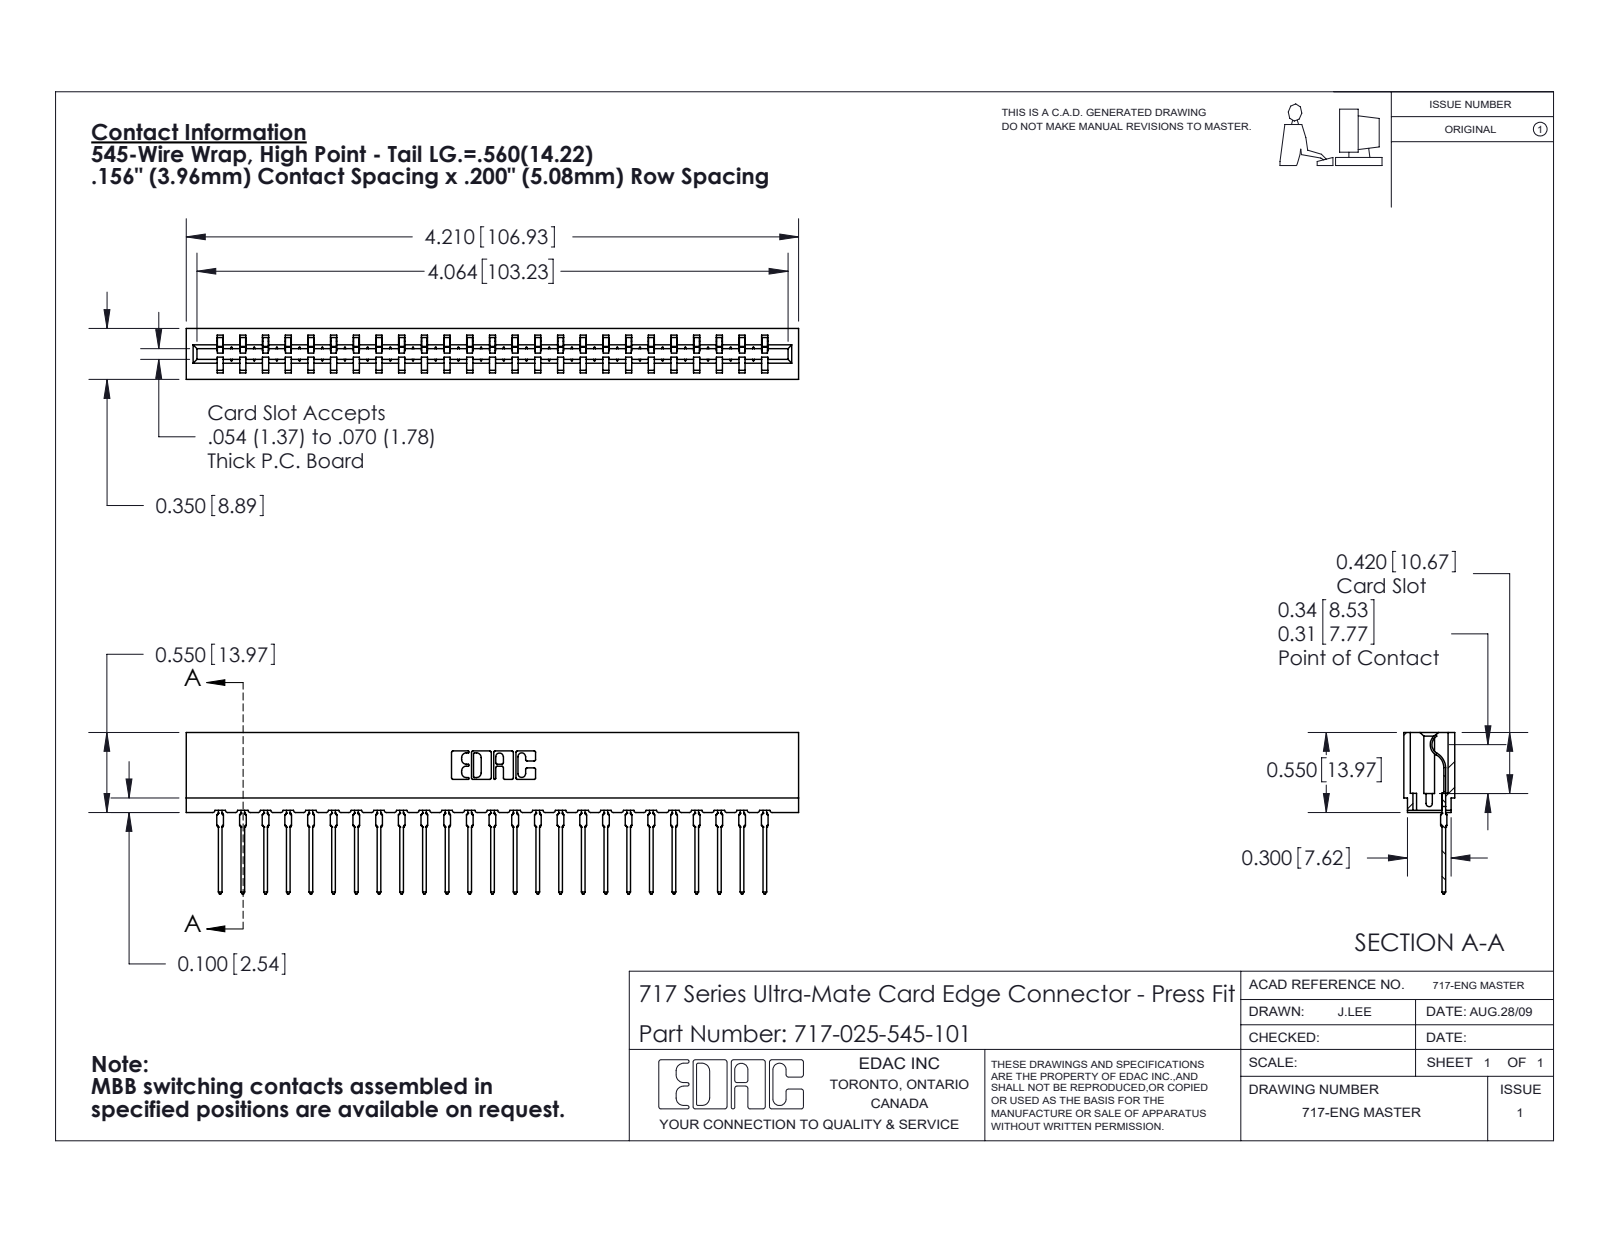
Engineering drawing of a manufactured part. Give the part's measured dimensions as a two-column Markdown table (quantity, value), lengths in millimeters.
| quantity | value |
| --- | --- |
| part name | 717 Part_Insulator Option - 06; 717-025-545-101; 745-292-001_545 |
| STEP written by | SolidWorks 2020 (CONFIG_CONTROL_DESIGN) |
| units | millimeters |
| bodies | 26 solids, 2919 faces (1754 planar, 515 cylindrical, 650 other) |
| overall size | 106.9 × 28.2 × 8.9 |
| volume | 9 180 mm³ |
| surface area | 13 100 mm² |
| partial cylindrical surfaces (radius × count) | 0.4 × 50, 0.5 × 50, 0.3 × 22, 0.2 × 6, 0.8 × 6, 0.1 × 4, 0.3 × 4, 0.7 × 3 |
| main face-to-face distances | 5.4, 3.5, 8.9, 4, 1.9, 1.6, 7.3, 1.9, 3.8, 15.8 |
